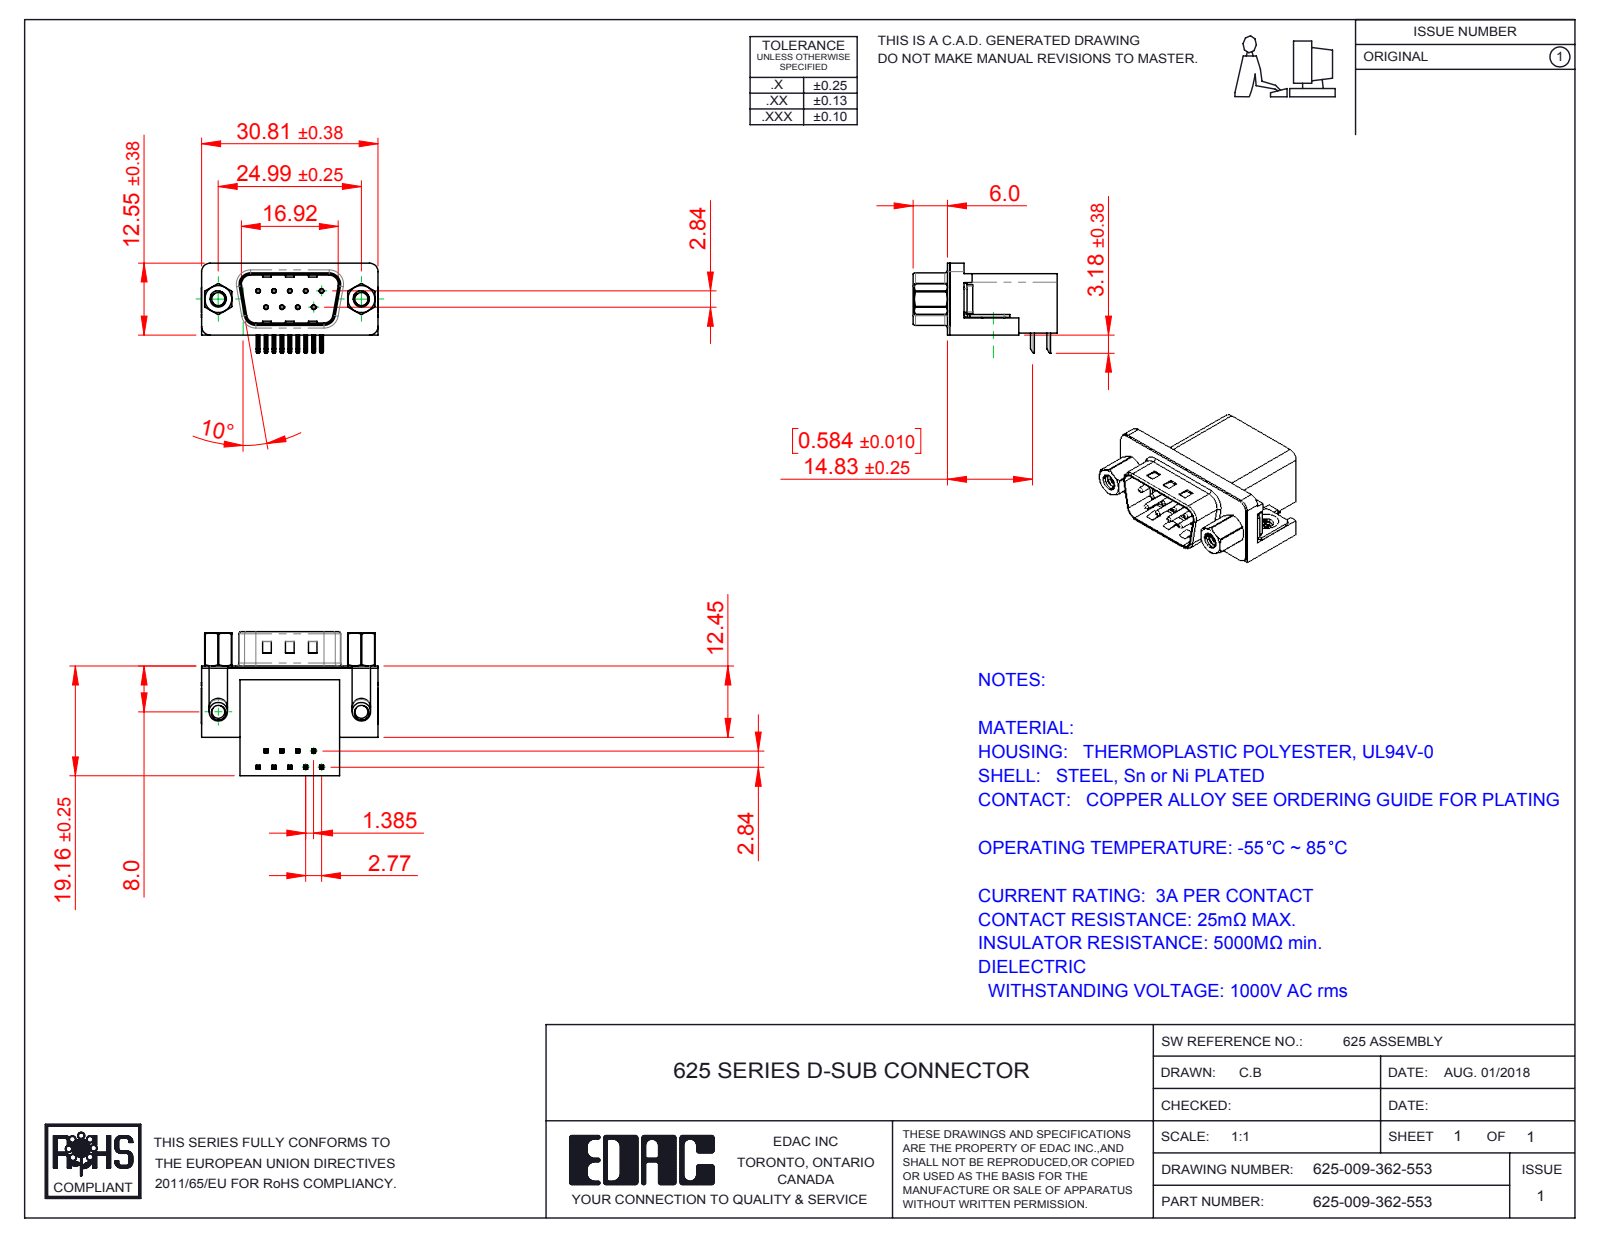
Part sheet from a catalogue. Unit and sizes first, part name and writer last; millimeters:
Units: millimetres
Overall size (bounding box): 30.89 × 25.16 × 15.73
Round holes (diameter × count): ⌀0.35 ×9, ⌀0.8 ×9, ⌀2.26 ×4, ⌀2.29 ×2, ⌀4 ×2, ⌀4.8 ×2, ⌀5 ×2
Round bosses / shafts (diameter × count): ⌀0.75 ×9, ⌀4.9 ×2, ⌀4.75 ×2, ⌀3.9 ×2, ⌀3.26 ×2, ⌀2.79 ×2
Partial cylindrical surfaces — rounded edges, fillets, slot ends (radius × count): R0.25 ×44, R0.12 ×18, R1 ×16, R0.5 ×9, R1.5 ×8, R1.6 ×8, R0.9 ×4, R2 ×4
Main face-to-face distances: 0.4, 10.34, 18.76, 19.16, 16.26, 2.5, 2.9, 0.35, 10.69, 6.7
Hole centre spacings: 3.16, 2.77, 5.54, 5.03, 5.04, 8.31, 7.48, 7.49
Volume: 4 700 mm³ · Surface area: 5 514 mm²
Bodies: 17 solids, 1151 faces (597 planar, 401 cylindrical, 153 other)
Part name (STEP PRODUCT): 625 Contact Bottom; 625 Shell_9 Socket; 625 4-40 Threaded Rivet; 625 4-40 Threaded Board Mount (+4 more)
STEP written by: SolidWorks 2016 (CONFIG_CONTROL_DESIGN)
